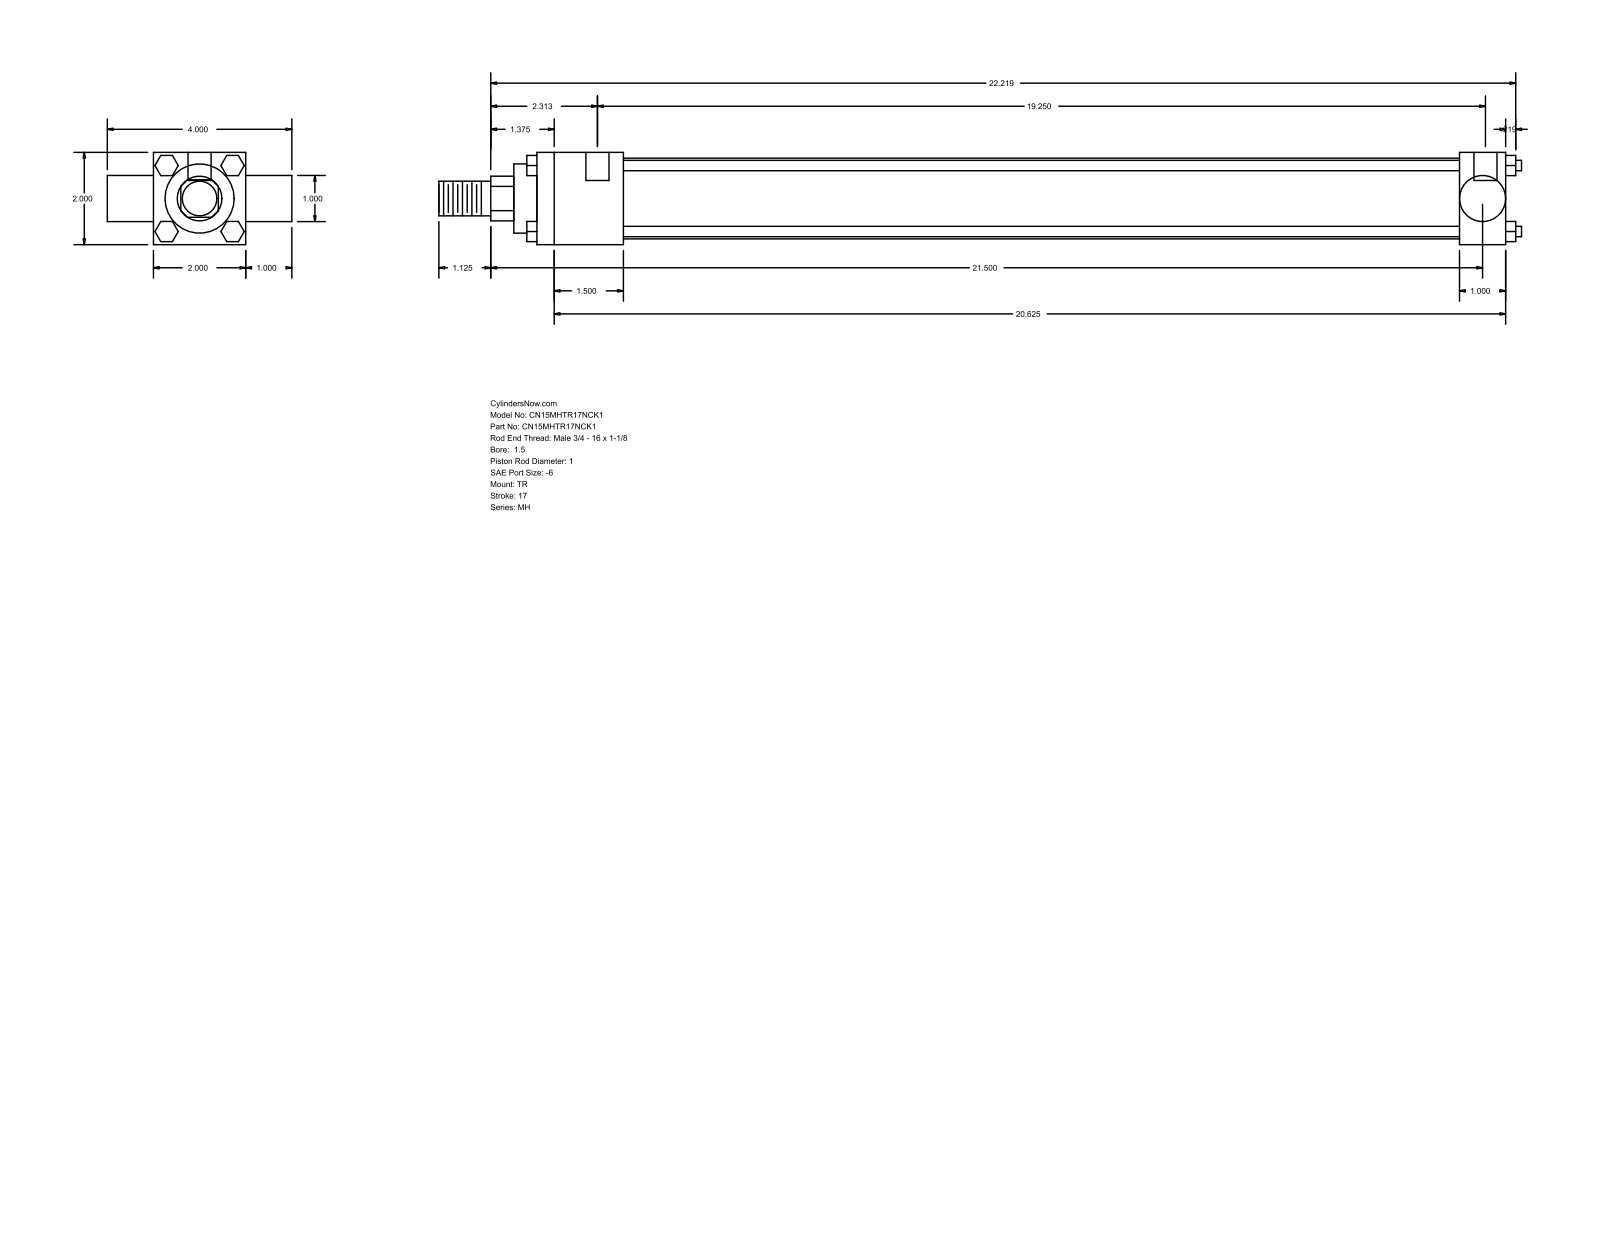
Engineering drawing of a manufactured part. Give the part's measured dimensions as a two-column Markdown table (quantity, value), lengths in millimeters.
| quantity | value |
| --- | --- |
| part name | MH_TR__0150_1 |
| STEP written by | GSSL Pune (CONFIG_CONTROL_DESIGN) |
| units | millimeters |
| bodies | 0 solids, 120 faces (92 planar, 28 cylindrical, 0 other) |
| overall size | 596.11 × 101.6 × 50.8 |
| round holes (diameter × count) | 5.56 × 3, 12.7 × 2 |
| round bosses / shafts (diameter × count) | 5.71 × 4, 44.45 × 1, 38.1 × 1, 25.4 × 1, 25.35 × 1, 19.05 × 1 |
| partial cylindrical surfaces (radius × count) | 12.29 × 1 |
| main face-to-face distances | 50.8, 25.4, 533.4, 76.2, 47.63, 485.77, 508, 460.37, 101.6, 12.7 |
| hole center spacings | 3.18, 488.95, 492.13 |
